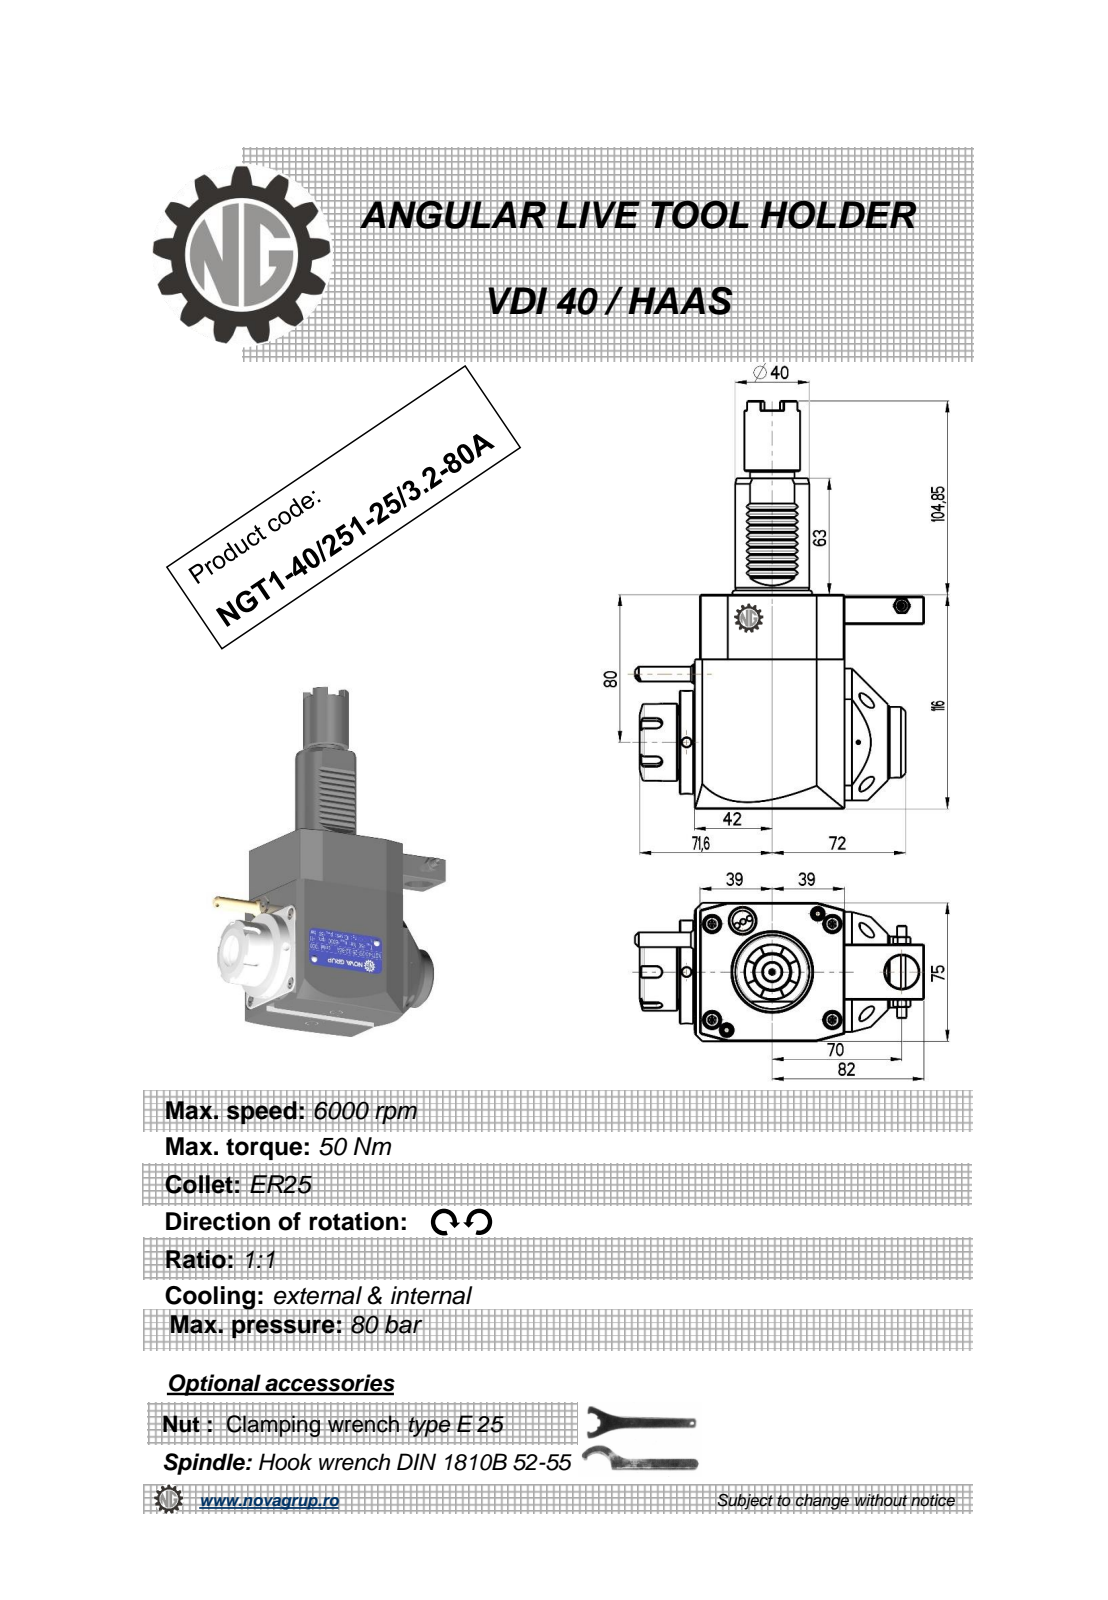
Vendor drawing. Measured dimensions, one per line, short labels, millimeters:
name: NGT1_40_251_32_3_2_80A
written by: PRO/ENGINEER BY PARAMETRIC TECHNOLOGY CORPORATION, 2010280 (CONFIG_CONTROL_DESIGN)
unit: mm
bodies: 1 solid, 489 faces (224 planar, 103 cylindrical, 162 other)
size: 220.85 × 156.14 × 75
volume: 925 081 mm³; area: 79 569 mm²
holes: 3× ⌀5, 1× ⌀3, 1× ⌀4.2, 1× ⌀9.5, 1× ⌀18, 1× ⌀20.3, 1× ⌀38.8, 1× ⌀42
bosses: 1× ⌀56, 1× ⌀41.4, 1× ⌀40, 1× ⌀38.5, 1× ⌀38.2, 1× ⌀38, 1× ⌀36, 1× ⌀30
rounds: 12× R0.26, 10× R0.3, 6× R0.2, 5× R3, 1× R0.5, 1× R40
face distances: 75, 116, 3, 81, 78, 111, 11, 1, 2.8, 80.8
hole spacings: 39.58, 40.93, 72.5, 116.25, 137.8
